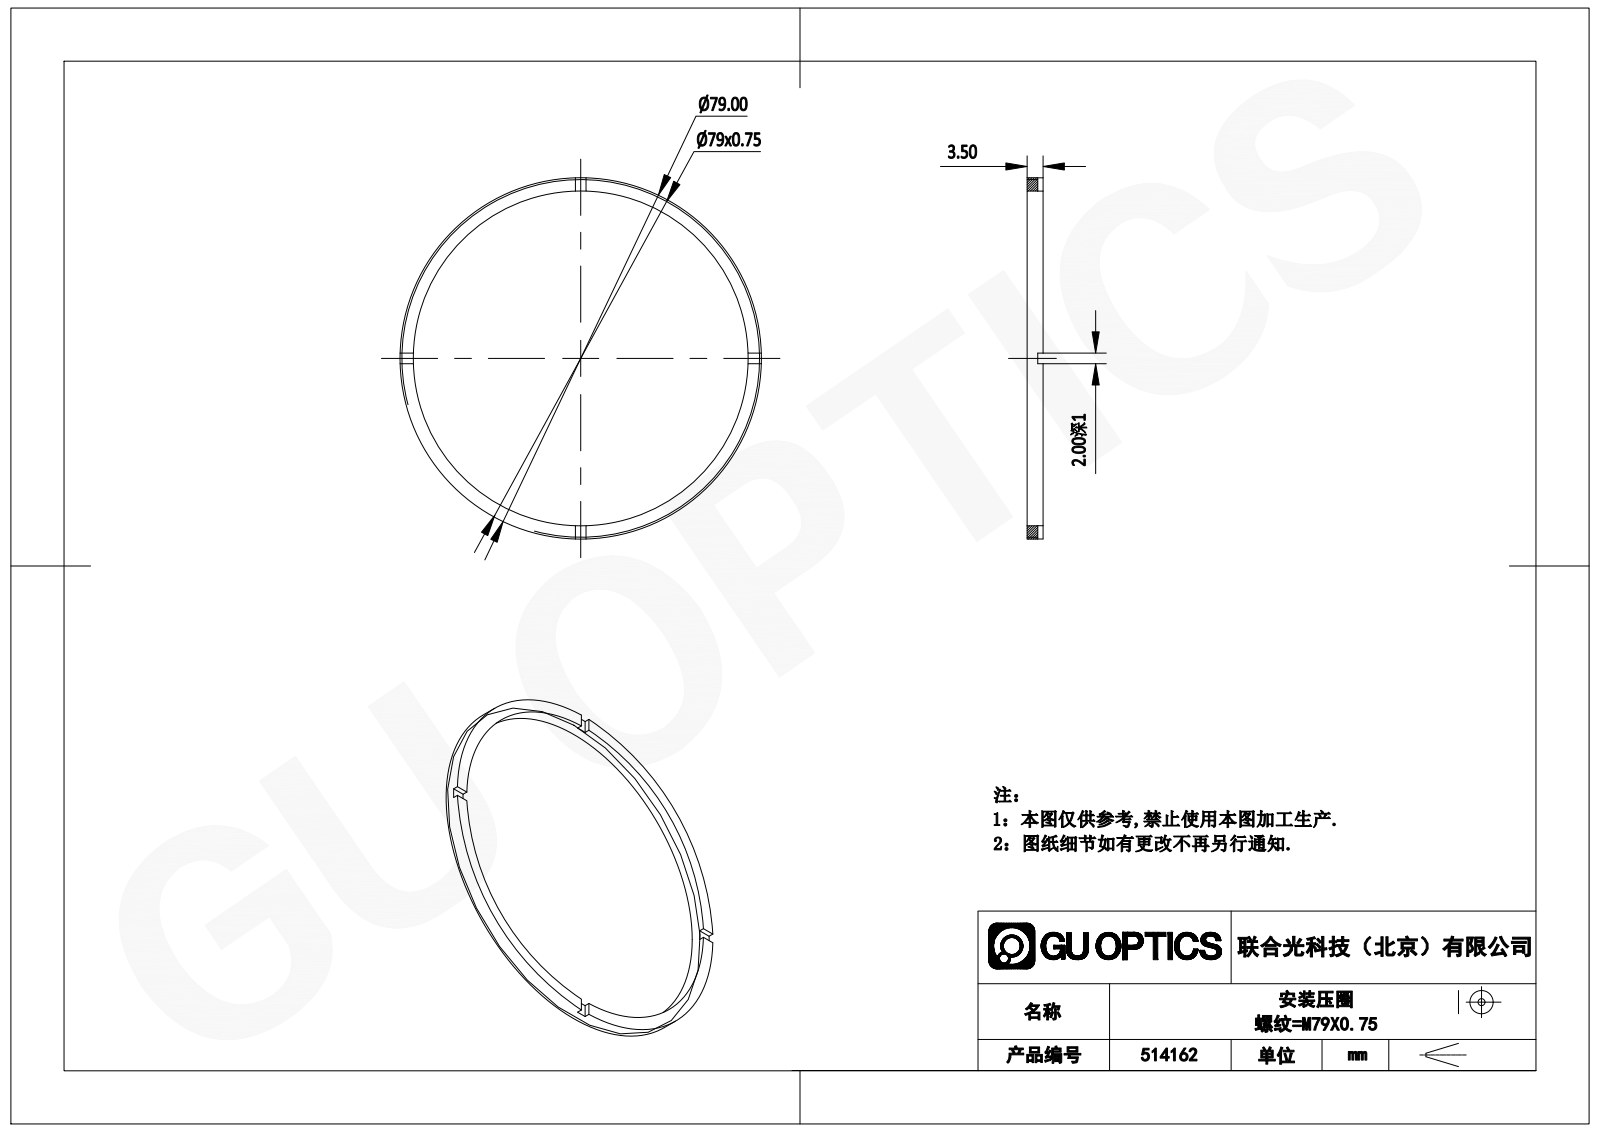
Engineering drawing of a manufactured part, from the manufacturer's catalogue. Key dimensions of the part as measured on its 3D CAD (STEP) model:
Part name (STEP PRODUCT): 514162
STEP written by: SolidWorks 2020 (CONFIG_CONTROL_DESIGN)
Units: millimetres
Bodies: 1 solid, 21 faces (17 planar, 4 cylindrical, 0 other)
Overall size (bounding box): 79 × 79 × 4
Volume: 2 841 mm³ · Surface area: 3 351 mm²
Round holes (diameter × count): ⌀73 ×1
Round bosses / shafts (diameter × count): ⌀79 ×1
Main face-to-face distances: 4, 3, 1, 2
